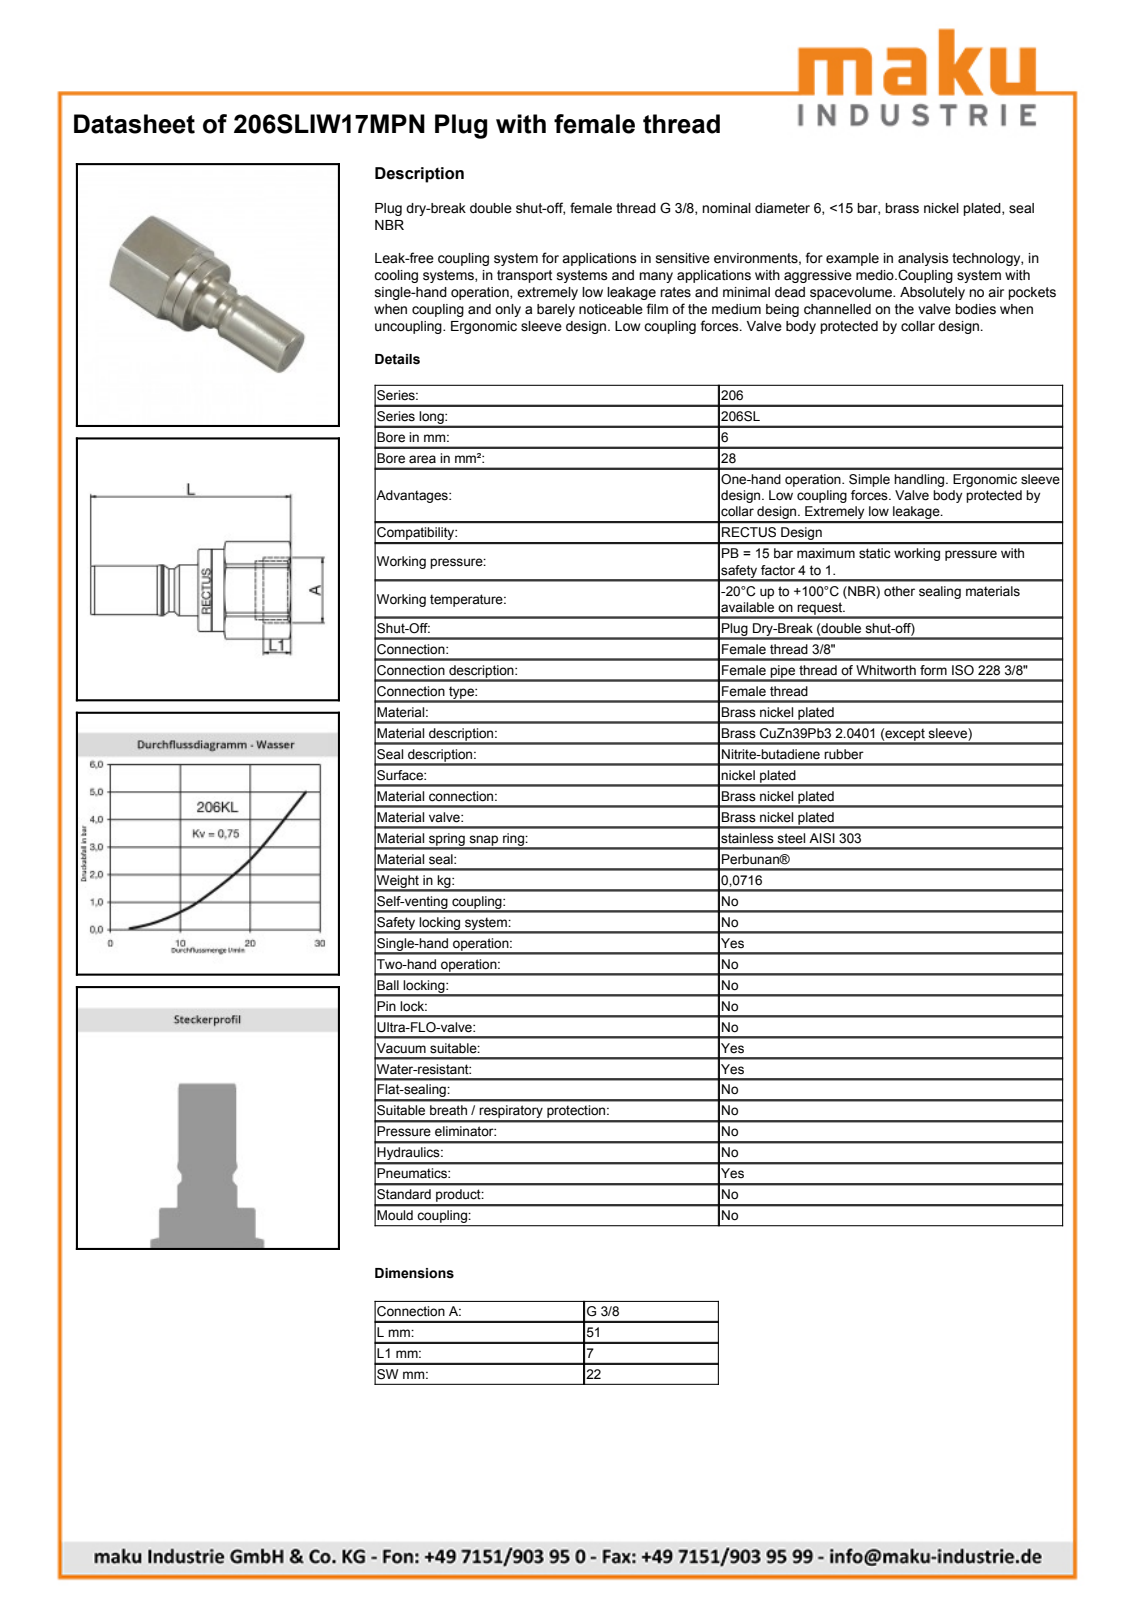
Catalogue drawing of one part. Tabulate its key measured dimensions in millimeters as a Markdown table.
| quantity | value |
| --- | --- |
| part name | D108801 |
| STEP written by | Autodesk Inventor 2013 (AUTOMOTIVE_DESIGN) |
| units | millimeters |
| bodies | 1 solid, 64 faces (17 planar, 19 cylindrical, 28 other) |
| overall size | 51.15 × 24.76 × 23.02 |
| volume | 11 131 mm³ |
| surface area | 4 461 mm² |
| round holes (diameter × count) | 10.2 × 1, 14.95 × 1, 17 × 1 |
| round bosses / shafts (diameter × count) | 21 × 1, 16.65 × 1, 15.38 × 1, 12.95 × 1, 12.5 × 1, 11 × 1 |
| partial cylindrical surfaces (radius × count) | 12.4 × 1 |
| main face-to-face distances | 22, 23.65, 27.5, 51.15, 42.15, 14.65, 9, 42.13, 14.63, 9.02 |
